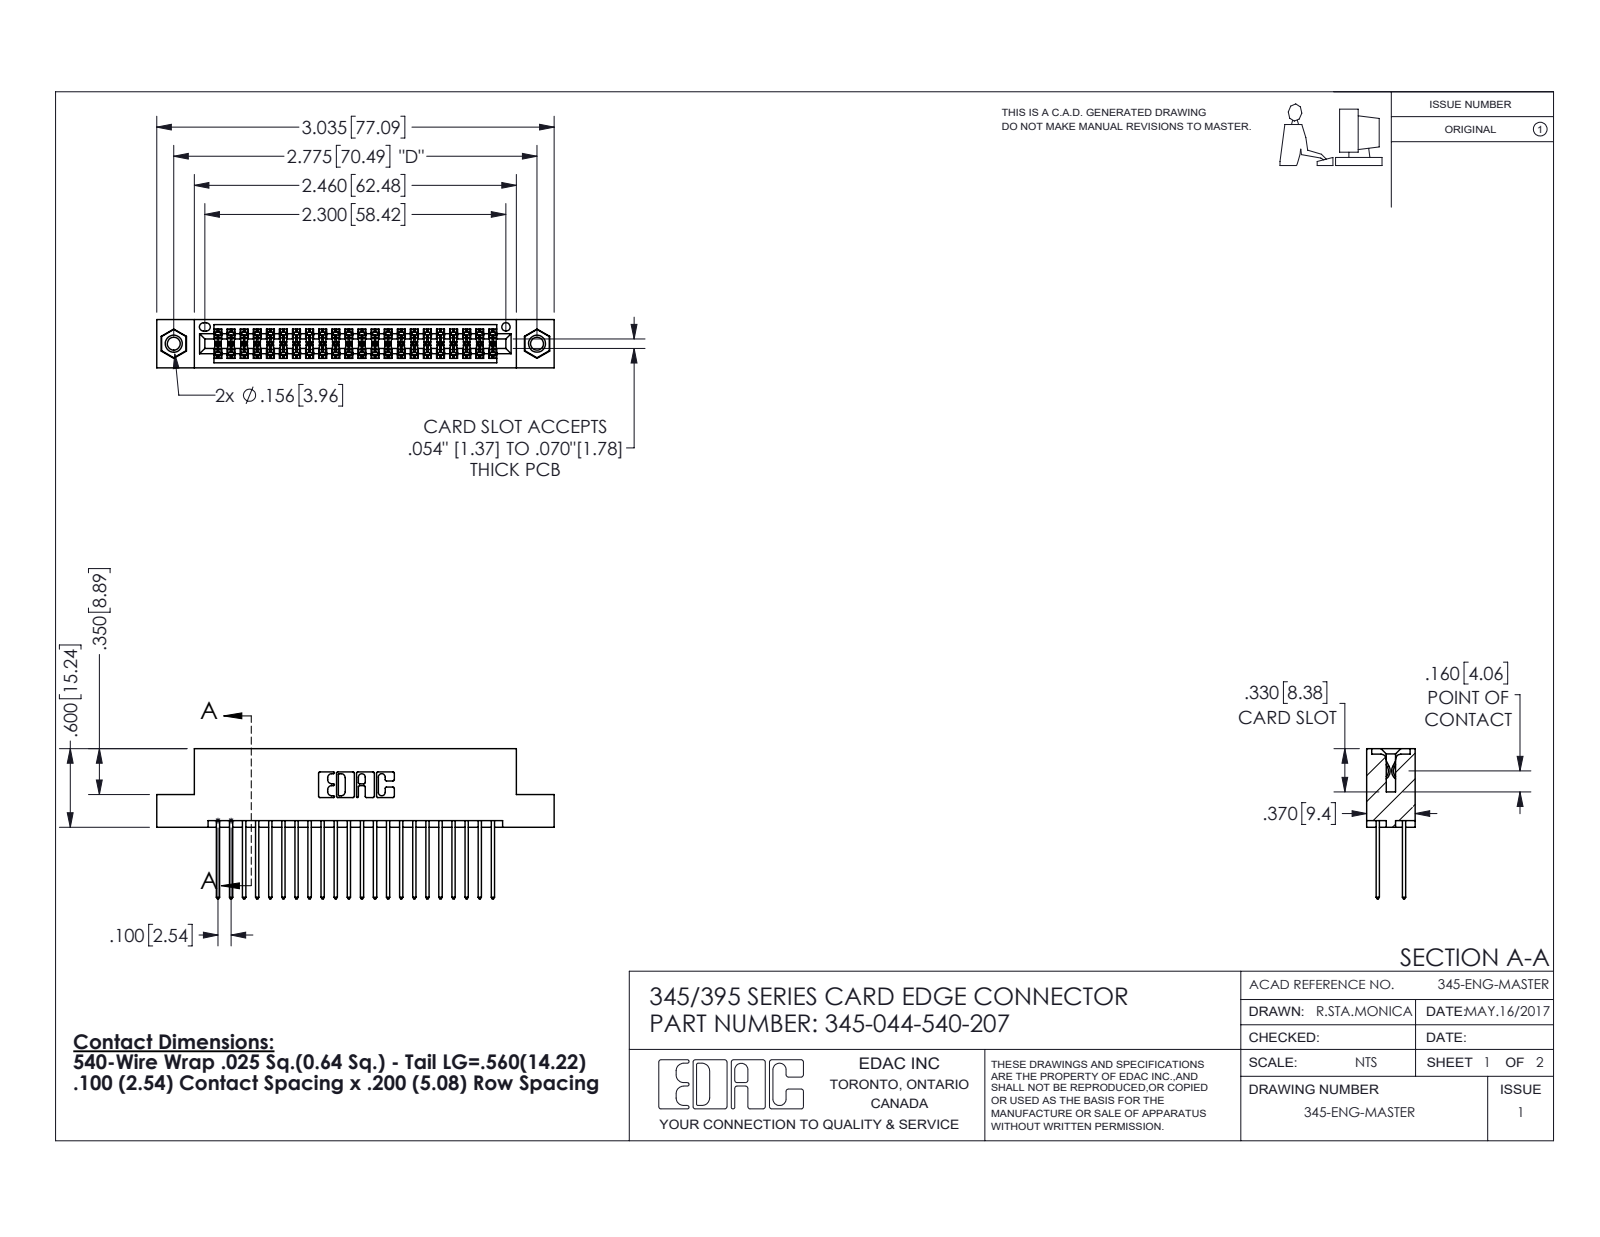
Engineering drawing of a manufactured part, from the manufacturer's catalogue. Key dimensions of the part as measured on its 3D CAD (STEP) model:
Part name (STEP PRODUCT): 345-250-001_345-250-005-103; 345 Part_Flush Mounting Lugs - 0.156 Dia-TI; 345-044-540-207; 345-292-001_345-293-140
STEP written by: SolidWorks 2016 (CONFIG_CONTROL_DESIGN)
Units: inches
Bodies: 47 solids, 2386 faces (1564 planar, 806 cylindrical, 16 other)
Overall size (bounding box): 3.035 × 1.147 × 0.37
Volume: 0.455 in³ · Surface area: 17.73 in²
Round holes (diameter × count): ⌀0.098 ×2, ⌀0.125 ×2, ⌀0.156 ×2, ⌀0.064 ×1
Round bosses / shafts (diameter × count): ⌀0.155 ×2
Partial cylindrical surfaces — rounded edges, fillets, slot ends (radius × count): R0.006 ×66, R0.01 ×44, R0.01 ×22, R0.007 ×6, R0.031 ×6, R0.026 ×3, R0.014 ×2, R0.019 ×2
Main face-to-face distances: 0.072, 0.298, 0.2, 0.098, 0.272, 0.025, 0.37, 0.225, 0.175, 0.149
Hole centre spacings: 0.27, 2.541, 2.775
